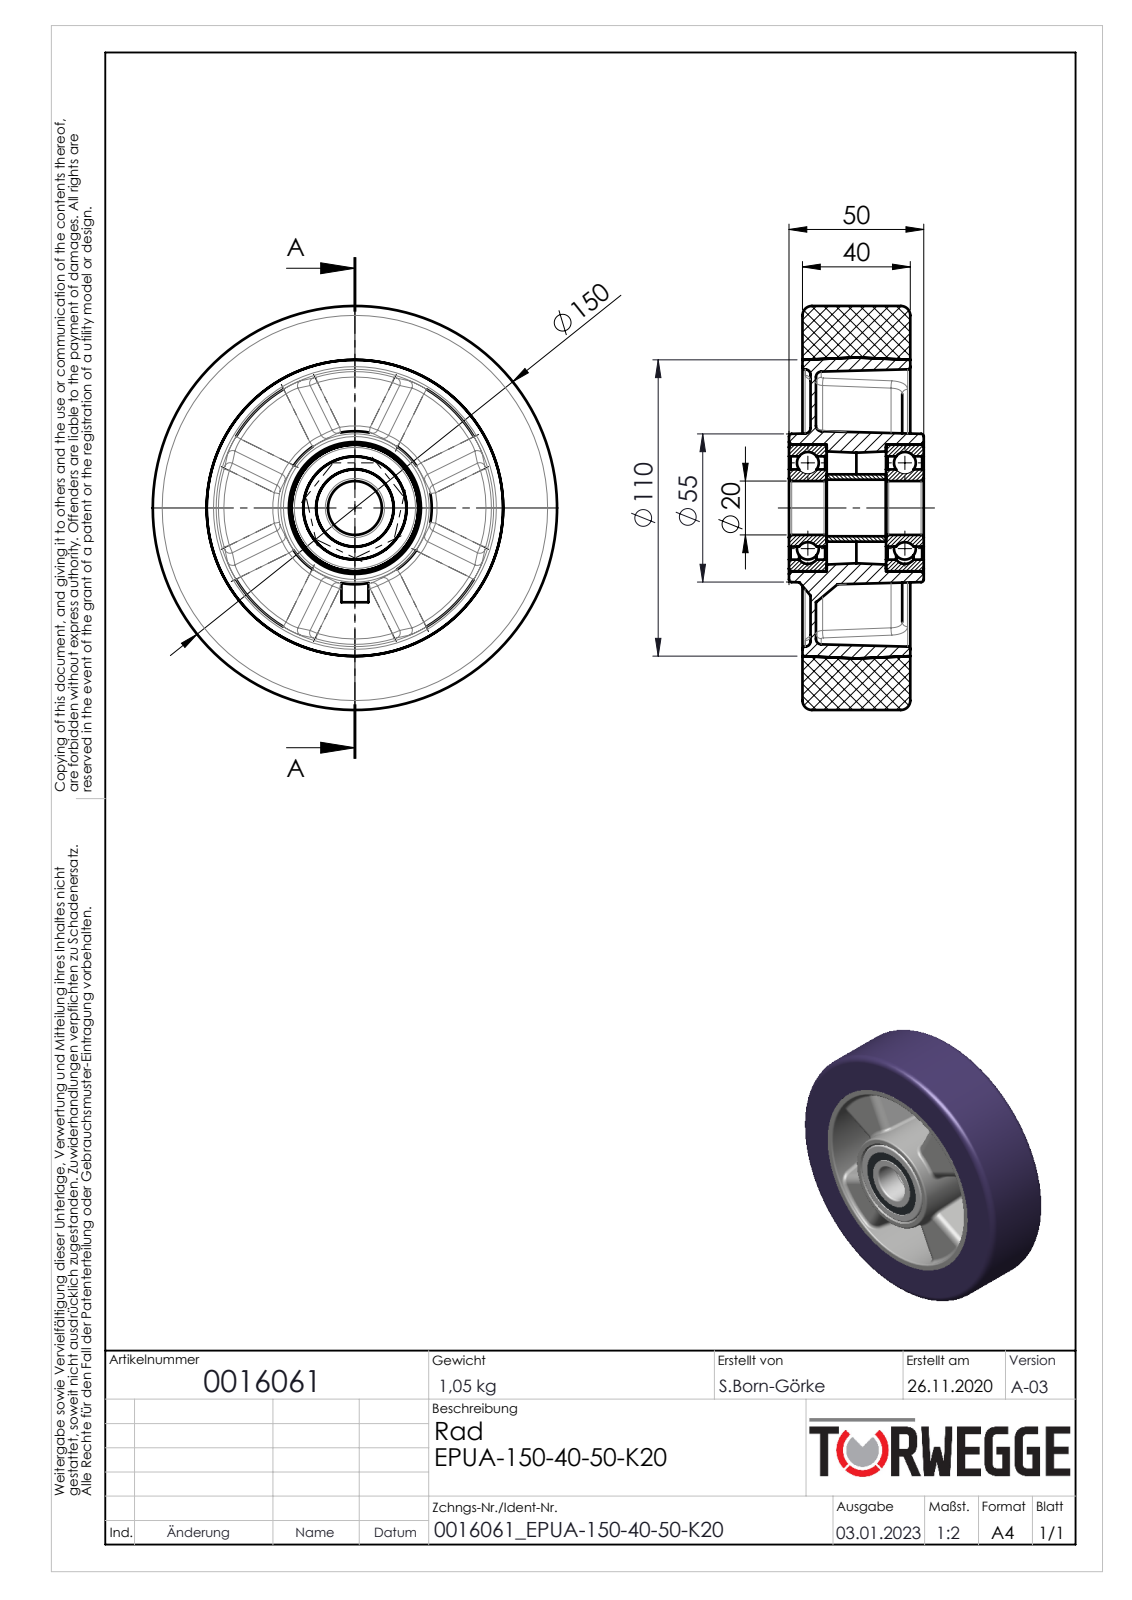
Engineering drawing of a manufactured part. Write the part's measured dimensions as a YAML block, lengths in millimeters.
part_name: "0016061"
step_written_by: "SolidWorks 2020 (AUTOMOTIVE_DESIGN)"
units: millimeters
bodies: {solids: 9, faces: 419, planar: 65, cylindrical: 82, other: 272}
overall_size: [150, 150, 50]
volume: 472163
surface_area: 137151
round_holes:
  - {diameter: 20, count: 1}
  - {diameter: 21, count: 1}
  - {diameter: 28.84, count: 1}
  - {diameter: 38.36, count: 1}
  - {diameter: 47, count: 1}
round_bosses_or_shafts:
  - {diameter: 150, count: 1}
  - {diameter: 38.16, count: 1}
  - {diameter: 28.64, count: 1}
  - {diameter: 25, count: 1}
partial_cylinders:
  - {radius: 3, count: 16}
  - {radius: 5, count: 16}
face_to_face_distances: [40, 2, 5, 36, 3, 37, 35, 32, 9, 31]
